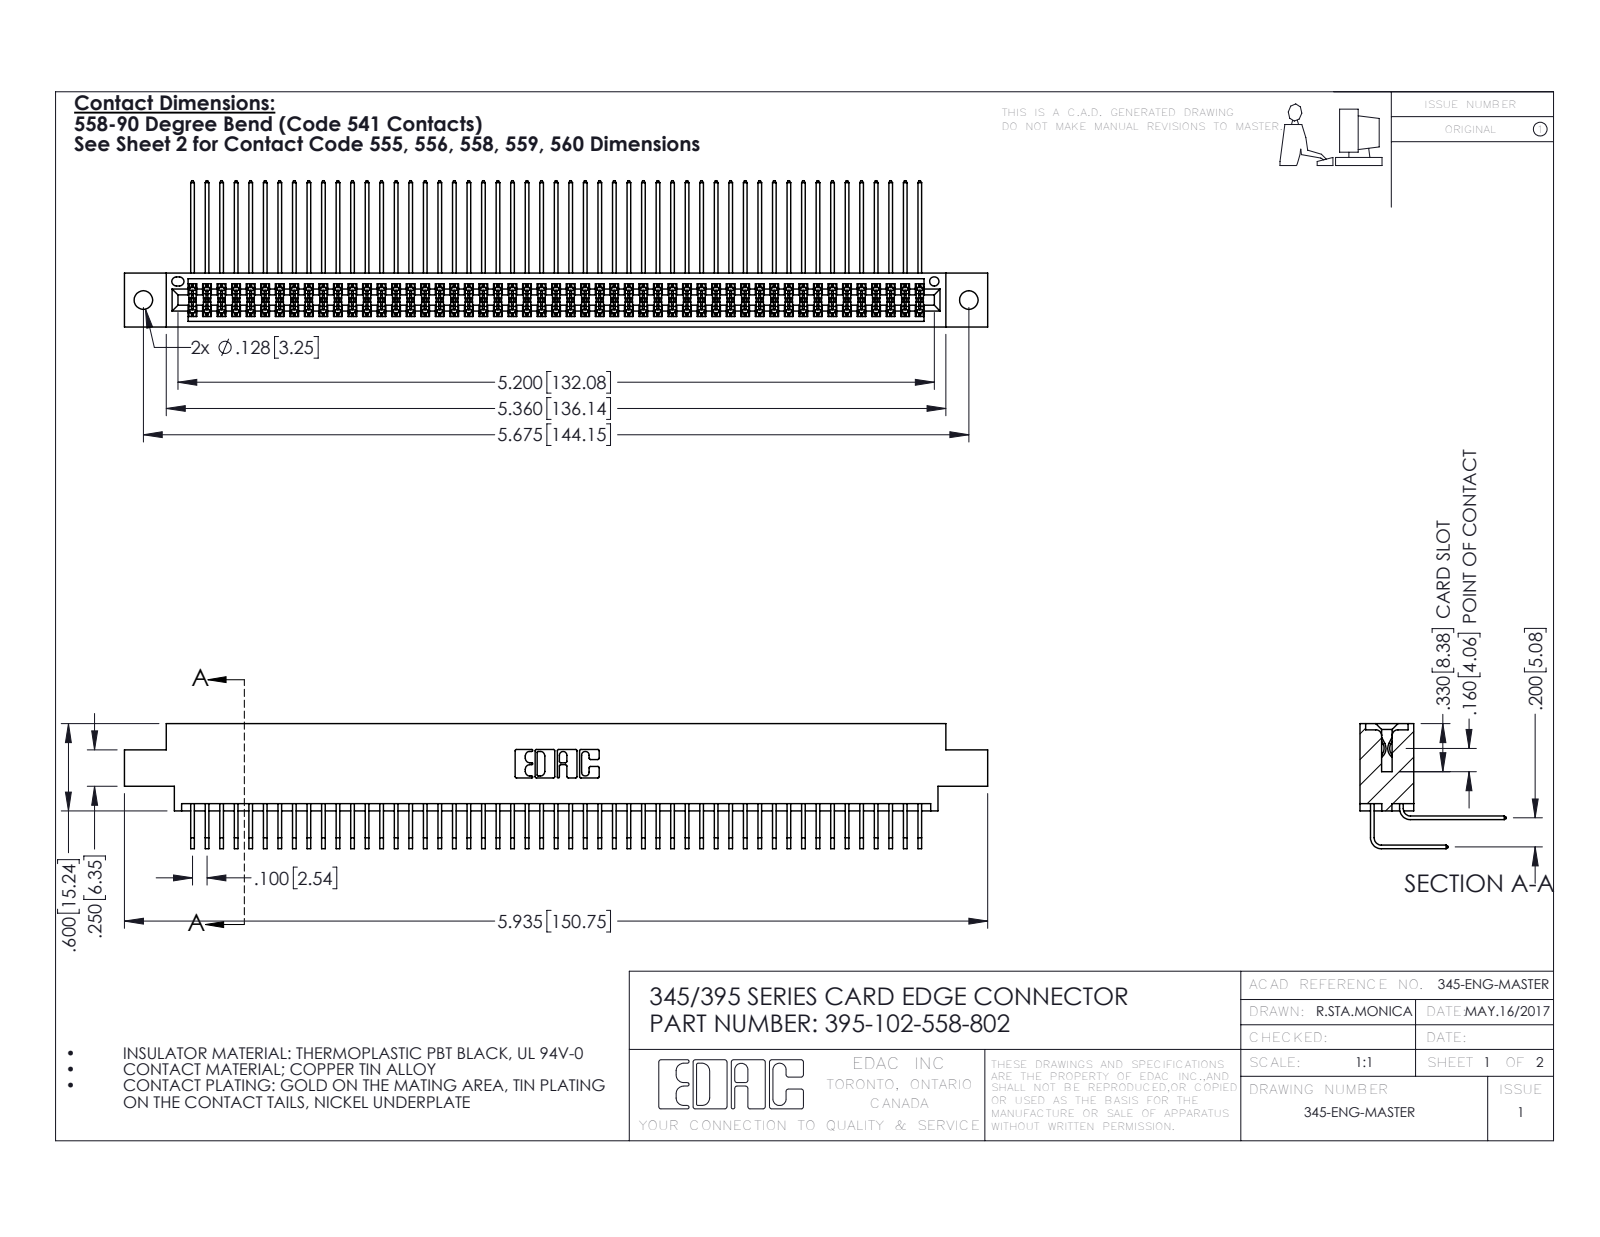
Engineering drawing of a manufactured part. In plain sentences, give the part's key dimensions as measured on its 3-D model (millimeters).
The part is named "345 Part_0.170 Offset - 0.128 Dia; 345-292-001_558 Tail - 2; 345-292-001_558 559 Tail - 1; 395-102-558-802". Its 3-D file was written by "SolidWorks 2016 (CONFIG_CONTROL_DESIGN)". It is 103 solids with 5434 faces: 3654 planar, 1780 cylindrical and 0 other. Overall it measures 150.7 by 25.5 by 21.8 millimeters. Its volume is 15 200 cubic millimeters and its surface area 25 230 square millimeters. Round holes: 2 of diameter 3.3, 1 of diameter 1.6. Partial cylindrical surfaces (rounded edges, fillets, slot ends): 154 of radius 0.2, 22 of radius 0.3, 6 of radius 0.2, 6 of radius 0.8, 3 of radius 0.7, 2 of radius 0.4, 2 of radius 0.5, 2 of radius 0.6. The main face-to-face distances are 1.8, 7.6, 5.1, 9.4, 2.5, 6.9, 0.6, 5.7, 4.4, 0.6. The hole center spacings are 6.9, 138.2, 144.1.
